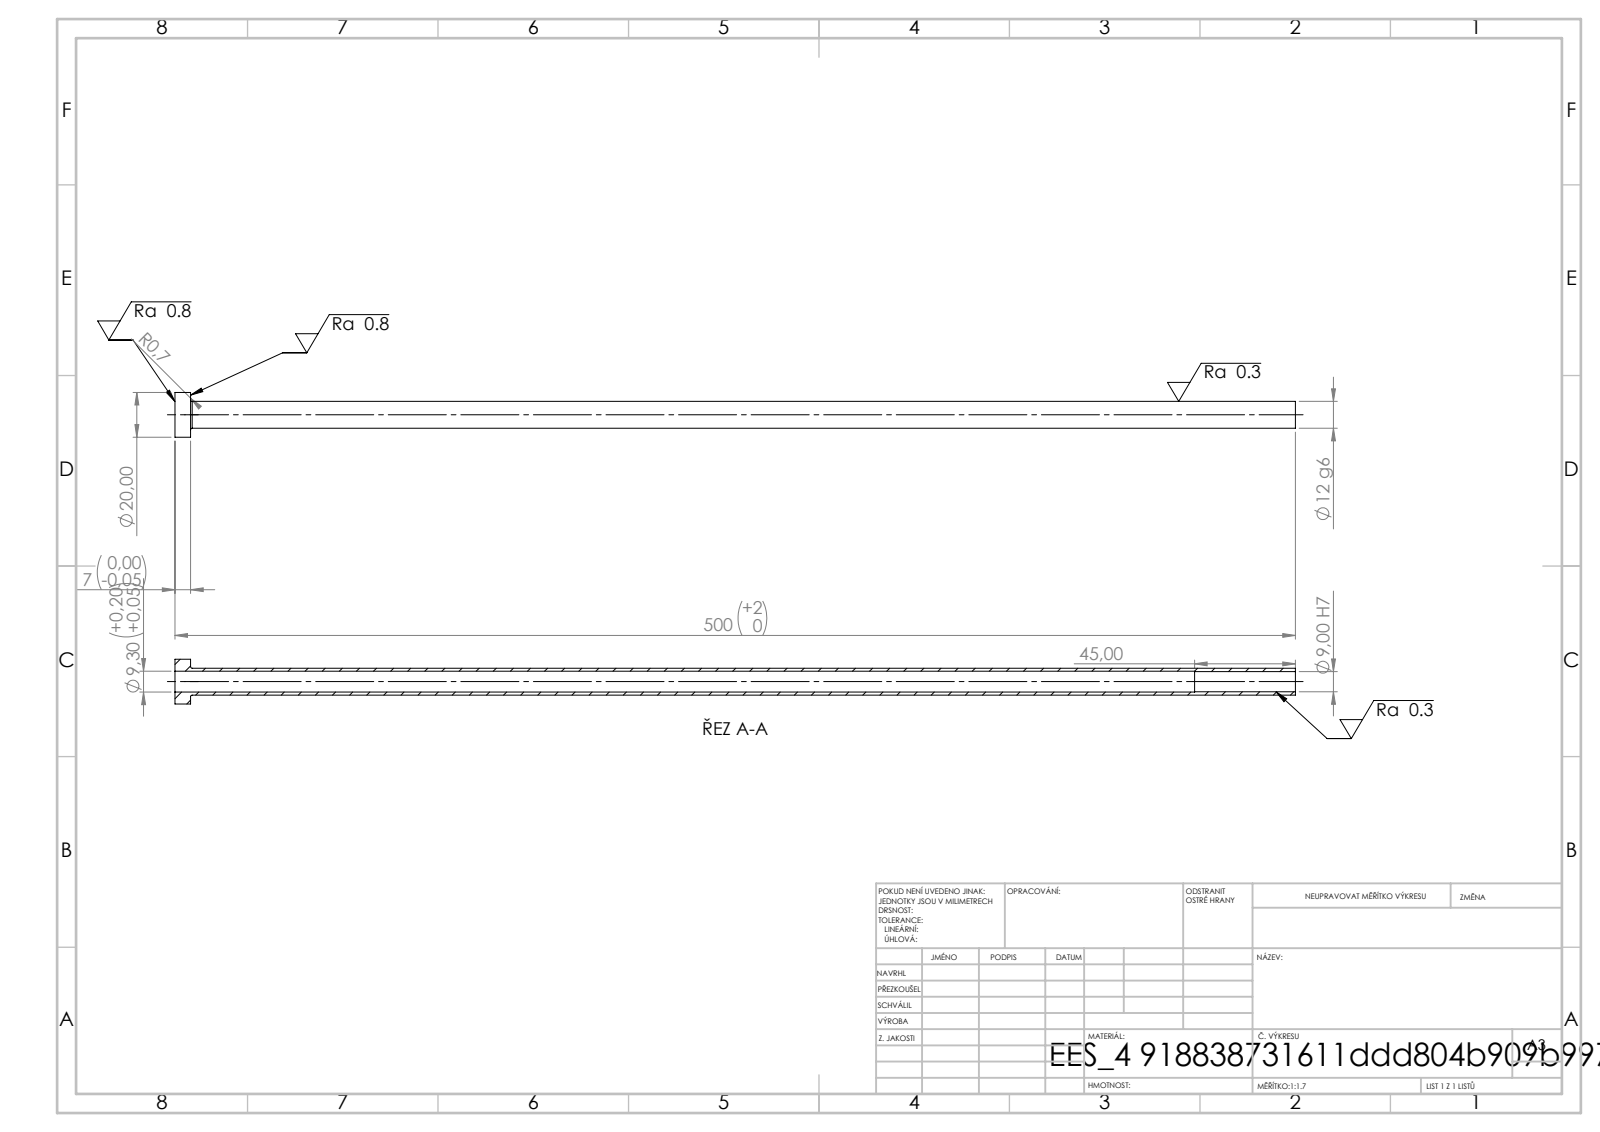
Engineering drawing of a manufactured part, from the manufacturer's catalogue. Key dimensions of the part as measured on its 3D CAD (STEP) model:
STEP written by: SolidWorks 2019 (CONFIG_CONTROL_DESIGN)
Units: millimetres
Bodies: 1 solid, 14 faces (4 planar, 8 cylindrical, 2 other)
Overall size (bounding box): 500 × 20 × 20
Volume: 24 190 mm³ · Surface area: 34 081 mm²
Round holes (diameter × count): ⌀9 ×1, ⌀9.3 ×1
Round bosses / shafts (diameter × count): ⌀20 ×1, ⌀12 ×1
Main face-to-face distances: 7, 500, 493, 455, 448, 45
